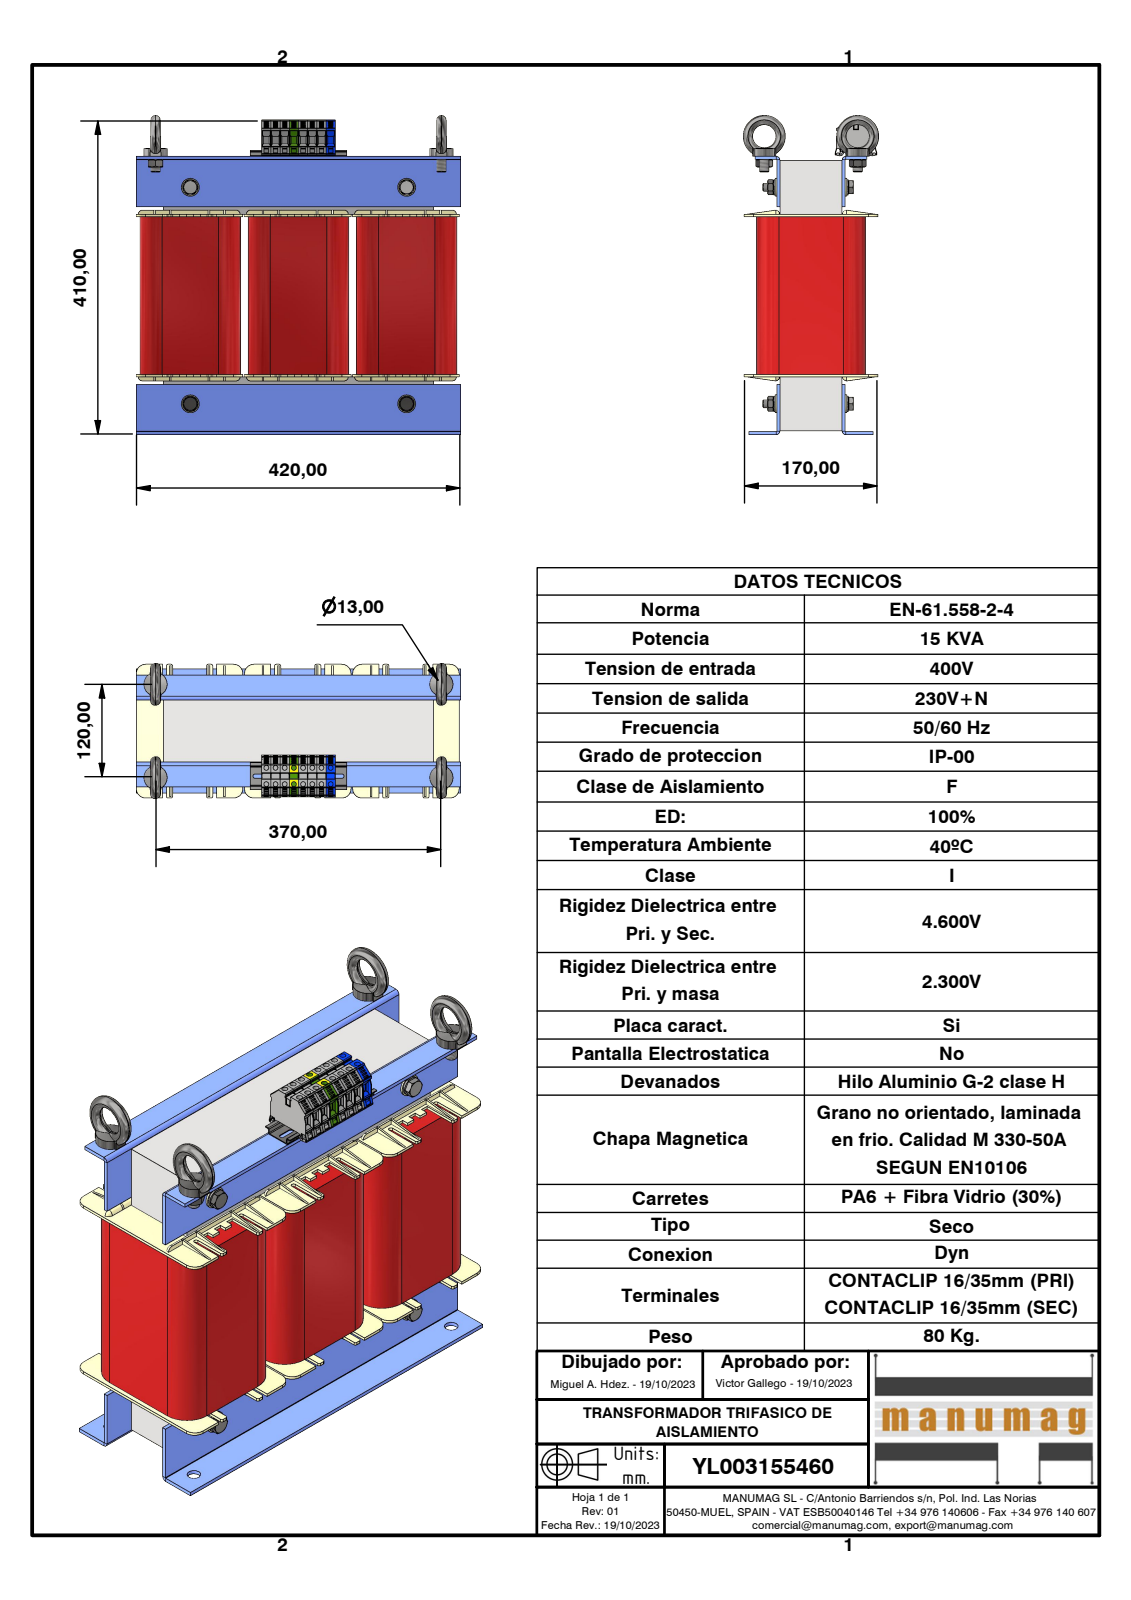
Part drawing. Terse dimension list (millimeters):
name: YL003155460; 3UI210 350 x 350 - 80; UI 210_80_BOBINADO; RC70 NT070 INFERIOR (+8 more)
written by: Autodesk Inventor 2023 (AUTOMOTIVE_DESIGN)
unit: mm
bodies: 47 solids, 4988 faces (2866 planar, 1698 cylindrical, 424 other)
size: 467 × 413 × 174
volume: 15 660 000 mm³; area: 1 953 000 mm²
holes: 16× ⌀6.3, 6× ⌀13, 6× ⌀15, 4× ⌀8.38, 4× ⌀10, 4× ⌀10.5, 4× ⌀14, 2× ⌀10.11, 2× ⌀30
bosses: 4× ⌀23, 4× ⌀20, 4× ⌀15.4, 4× ⌀12, 4× ⌀11.5, 4× ⌀10.8, 4× ⌀9.19, 2× ⌀54
rounds: 378× R0.3, 38× R2, 16× R0.25, 14× R1, 12× R2.5, 12× R2.92, 12× R12, 12× R28.5
face distances: 140, 70, 280, 84, 4, 210, 80, 3, 26.5, 113.5
hole spacings: 11.9, 24.14, 23.8, 31.74, 35.7, 41.42, 21, 47.6
